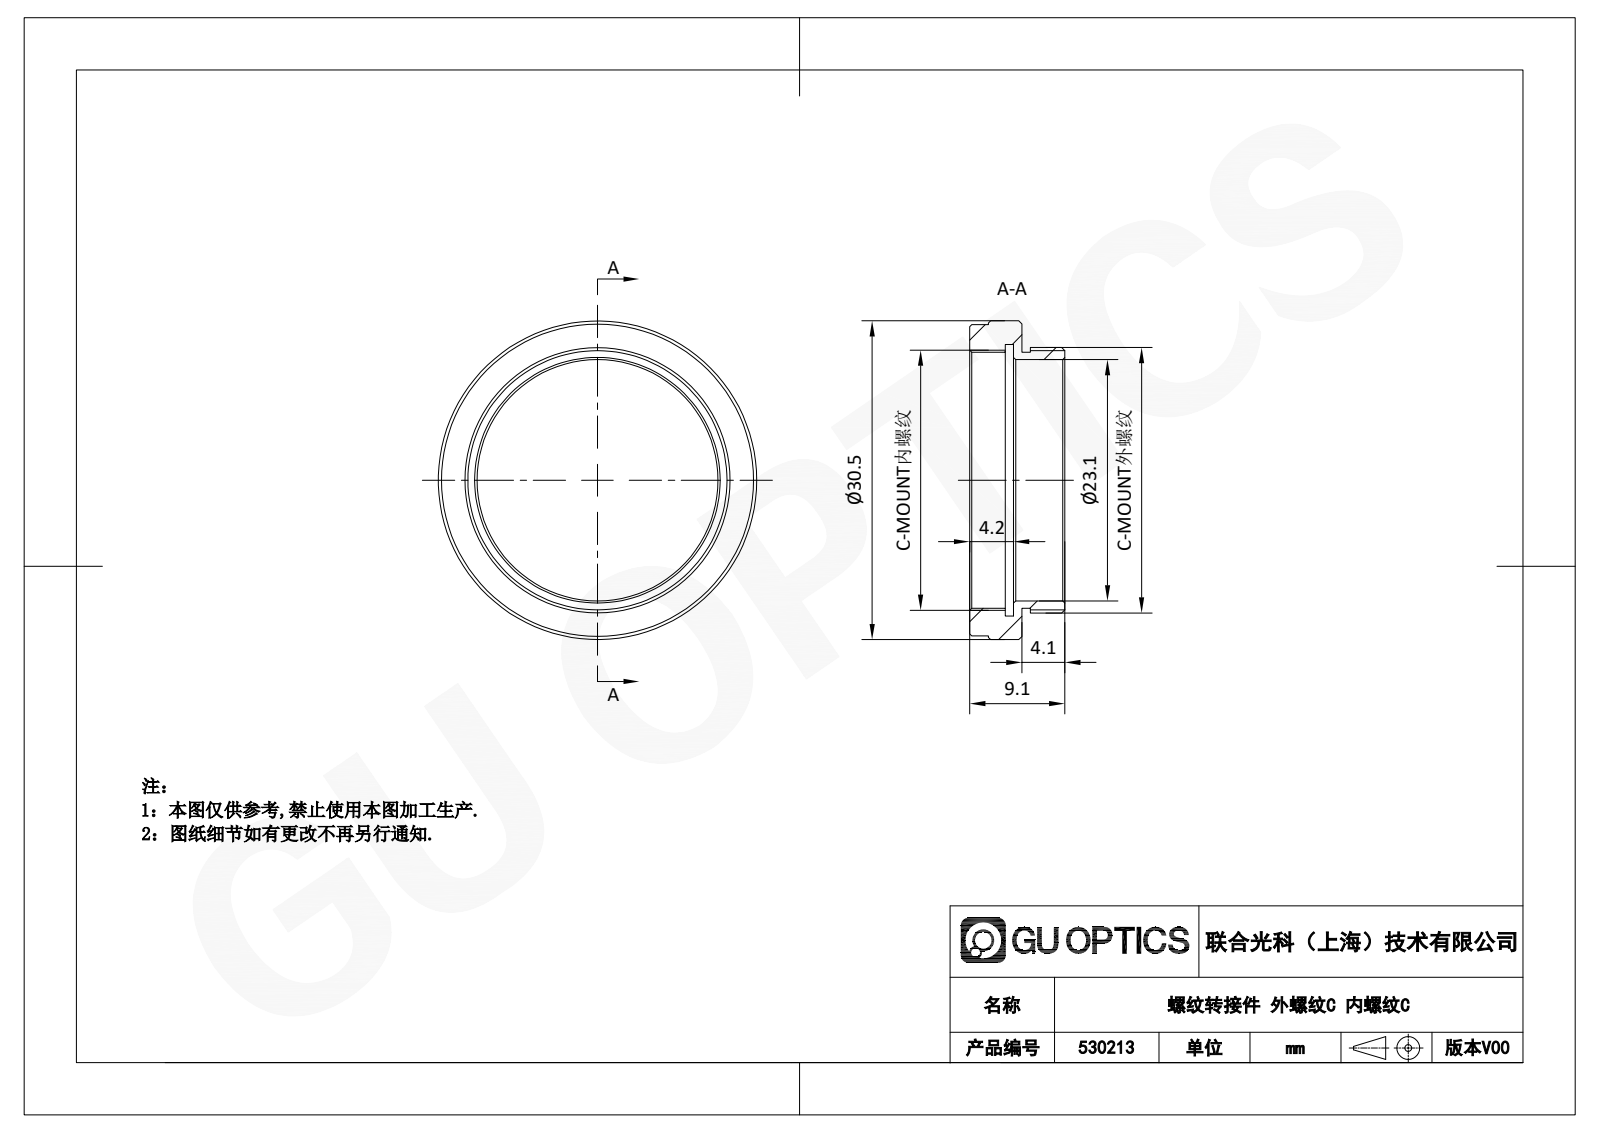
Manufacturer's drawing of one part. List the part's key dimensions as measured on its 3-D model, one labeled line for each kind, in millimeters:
Part name (STEP PRODUCT): 530213
STEP written by: SolidWorks 2020 (CONFIG_CONTROL_DESIGN)
Units: millimetres
Bodies: 1 solid, 21 faces (7 planar, 7 cylindrical, 7 other)
Overall size (bounding box): 30.5 × 30.5 × 9.1
Volume: 1 546 mm³ · Surface area: 2 217 mm²
Round holes (diameter × count): ⌀23.1 ×1, ⌀24.5 ×1, ⌀26 ×1
Round bosses / shafts (diameter × count): ⌀30.5 ×1, ⌀29.8 ×1, ⌀25.4 ×1
Main face-to-face distances: 0.8, 5, 1.6, 4.2, 3.4, 2.4, 9.1, 5.7, 4.9, 4.1
